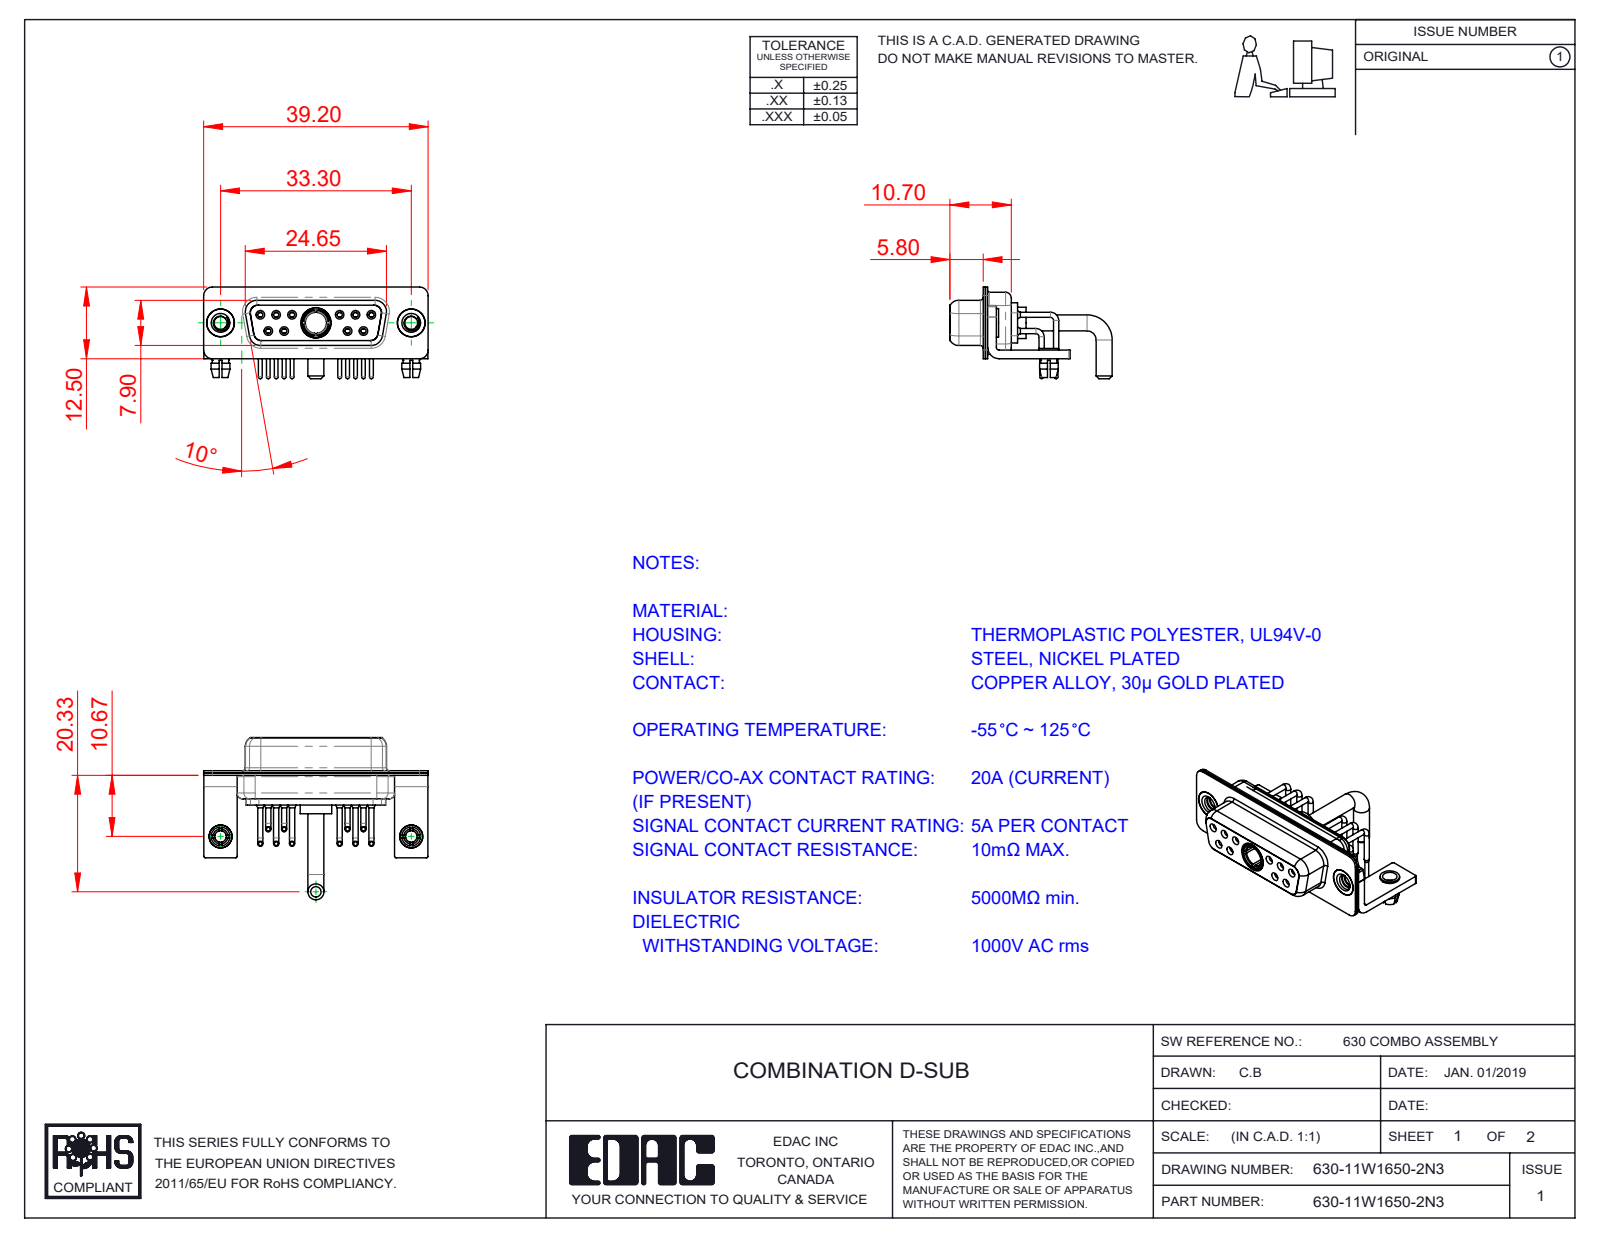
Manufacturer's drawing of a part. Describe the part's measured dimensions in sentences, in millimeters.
The part is named "630-11W1650-2N3; 630Combo Shell Rear_15 Contacts; 630Combo Contact Row 1; 630Combo Housing_11W1 (+6 more)". Its 3-D file was written by "SolidWorks 2020 (CONFIG_CONTROL_DESIGN)". It is 21 solids with 1019 faces: 314 planar, 442 cylindrical and 263 other. Overall it measures 39.2 by 28.33 by 16 millimeters. Its volume is 2 994 cubic millimeters and its surface area 7 132 square millimeters. Round holes: 12 of diameter 2, 10 of diameter 0.9, 10 of diameter 1.1, 10 of diameter 1.5, 6 of diameter 1.7, 4 of diameter 1.6, 3 of diameter 4.85, 2 of diameter 2.26, 2 of diameter 2.5, 2 of diameter 3.2, 2 of diameter 4, 2 of diameter 4.05. Round bosses or shafts: 10 of diameter 0.9, 10 of diameter 0.65, 6 of diameter 1.6, 2 of diameter 5, 2 of diameter 4.95, 2 of diameter 4.8, 2 of diameter 4, 2 of diameter 3.4. Partial cylindrical surfaces (rounded edges, fillets, slot ends): 16 of radius 0.25, 16 of radius 1.5, 13 of radius 2, 12 of radius 1.35, 8 of radius 1.6, 5 of radius 0.5, 4 of radius 0.6, 4 of radius 0.65. The main face-to-face distances are 0.4, 0.8, 0.45, 1.4, 8.45, 1.5, 1.8, 8.9, 6.2, 2.3. The hole center spacings are 3.16, 2.77, 13.85, 11.08, 16.62, 5.03, 5.04, 5.54.
